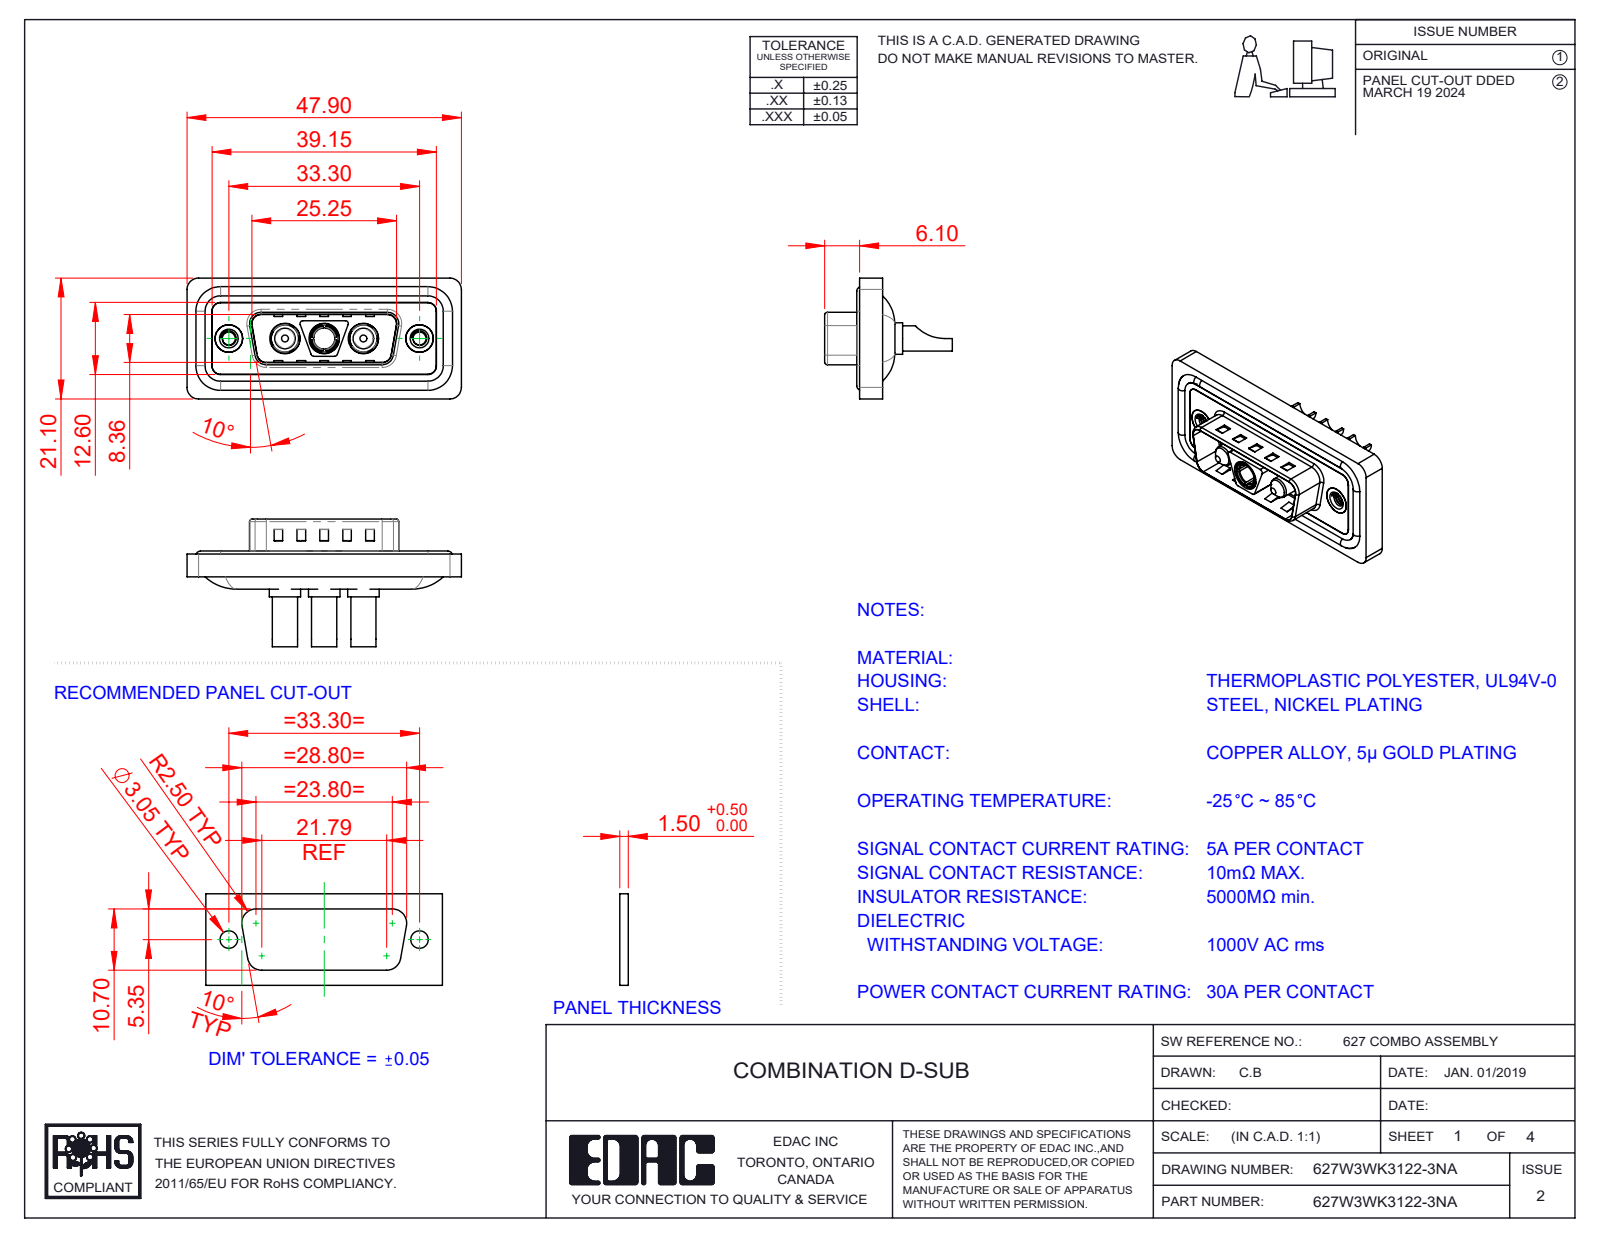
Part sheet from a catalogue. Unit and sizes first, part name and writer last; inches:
Units: inches
Overall size (bounding box): 1.886 × 0.878 × 0.831
Round holes (diameter × count): ⌀0.138 ×3, ⌀0.191 ×3, ⌀0.209 ×3, ⌀0.089 ×2, ⌀0.157 ×2, ⌀0.189 ×2, ⌀0.197 ×2, ⌀0.146 ×1
Round bosses / shafts (diameter × count): ⌀0.063 ×4, ⌀0.217 ×3, ⌀0.205 ×3, ⌀0.187 ×3, ⌀0.173 ×3, ⌀0.148 ×3, ⌀0.193 ×2, ⌀0.142 ×2
Partial cylindrical surfaces — rounded edges, fillets, slot ends (radius × count): R0.059 ×26, R0.079 ×20, R0.02 ×12, R0.063 ×8, R0.01 ×4, R0.024 ×4, R0.026 ×4, R0.035 ×4
Main face-to-face distances: 0.016, 0.043, 0.02, 0.063, 0.122, 0.059, 0.114, 0.032, 0.377, 0.098
Hole centre spacings: 0.27, 0.386, 0.656, 0.925, 0.539, 1.311
Volume: 0.352 in³ · Surface area: 14.64 in²
Bodies: 13 solids, 625 faces (240 planar, 261 cylindrical, 124 other)
Part name (STEP PRODUCT): 627Combo Waterproof Housing_15 Contacts; 627Combo Shell Front_15 Contacts; Power Socket_30A SC; 627Combo Shell Rear_15 Contacts (+4 more)
STEP written by: SolidWorks 2023 (CONFIG_CONTROL_DESIGN)
